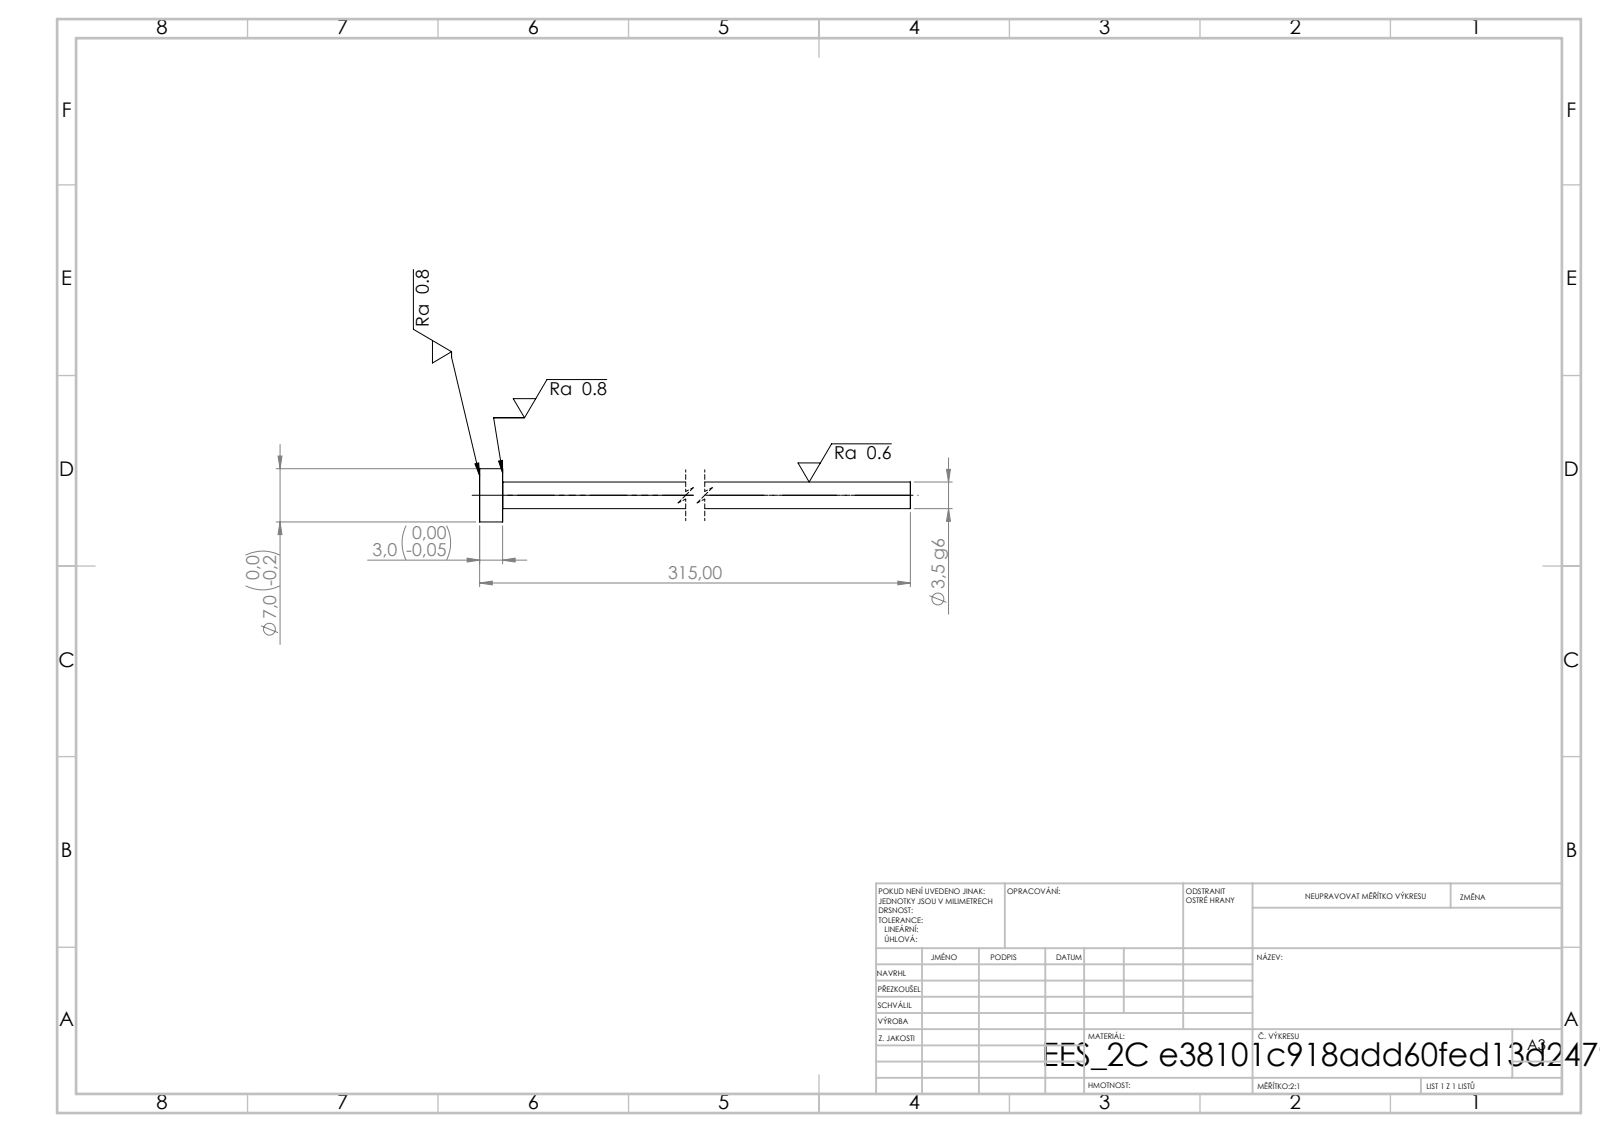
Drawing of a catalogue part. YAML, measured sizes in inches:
step_written_by: "SolidWorks 2019 (CONFIG_CONTROL_DESIGN)"
units: inches
bodies: {solids: 1, faces: 7, planar: 3, cylindrical: 4, other: 0}
overall_size: [12.402, 0.276, 0.276]
volume: 0.19
surface_area: 5.54
round_bosses_or_shafts:
  - {diameter: 0.276, count: 1}
  - {diameter: 0.138, count: 1}
face_to_face_distances: [0.118, 12.402, 12.283]
